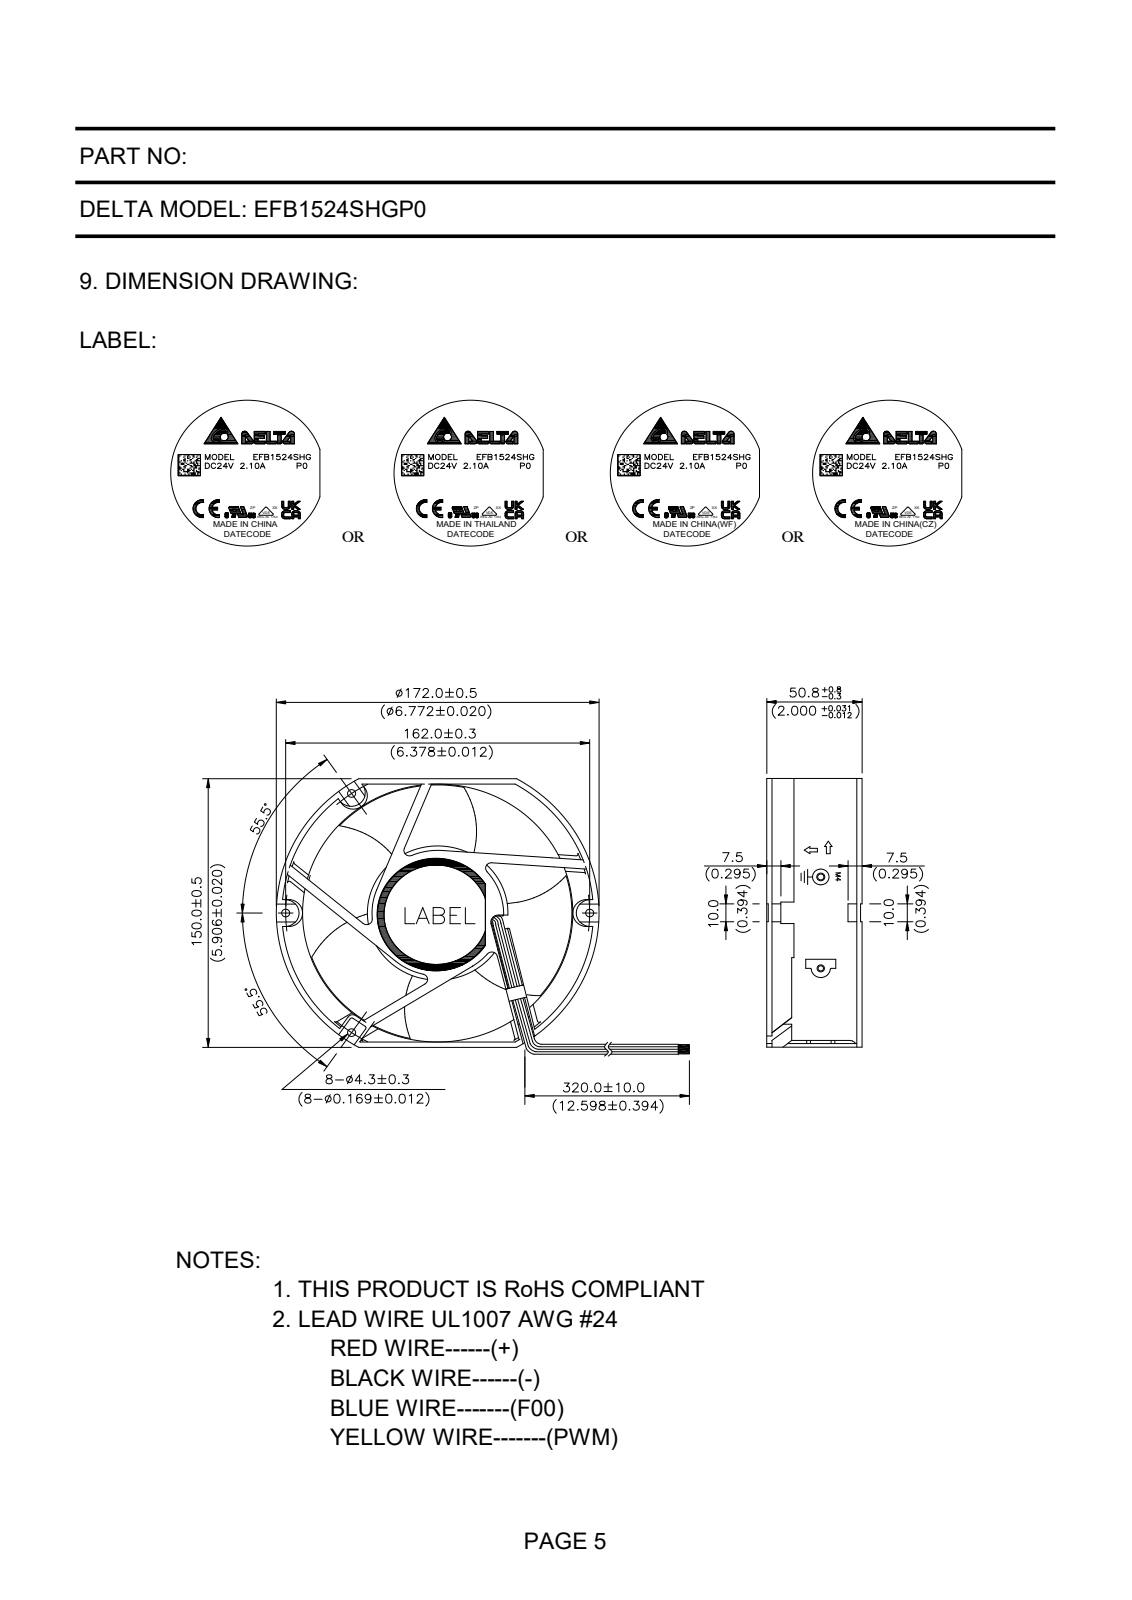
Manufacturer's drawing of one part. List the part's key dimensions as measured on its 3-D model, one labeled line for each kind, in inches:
Part name (STEP PRODUCT): PRT0013
STEP written by: CREO PARAMETRIC BY PTC INC, 2020454 (CONFIG_CONTROL_DESIGN)
Units: inches
Bodies: 1 solid, 419 faces (195 planar, 128 cylindrical, 96 other)
Overall size (bounding box): 6.772 × 5.906 × 2
Volume: 56.86 in³ · Surface area: 129.7 in²
Round holes (diameter × count): ⌀0.173 ×4, ⌀0.114 ×1, ⌀0.13 ×1
Round bosses / shafts (diameter × count): ⌀5.945 ×1, ⌀5.866 ×1
Partial cylindrical surfaces — rounded edges, fillets, slot ends (radius × count): R0.02 ×32, R0.039 ×13, R0.059 ×8, R0.197 ×5, R0.118 ×3, R0.19 ×1, R0.315 ×1, R1.378 ×1
Main face-to-face distances: 1.969, 0.031, 2, 0.11, 1.89, 1.858, 5.906, 0.079, 0.295, 1.705
Hole centre spacings: 2.97, 5.644, 2.022, 5.256, 6.378
